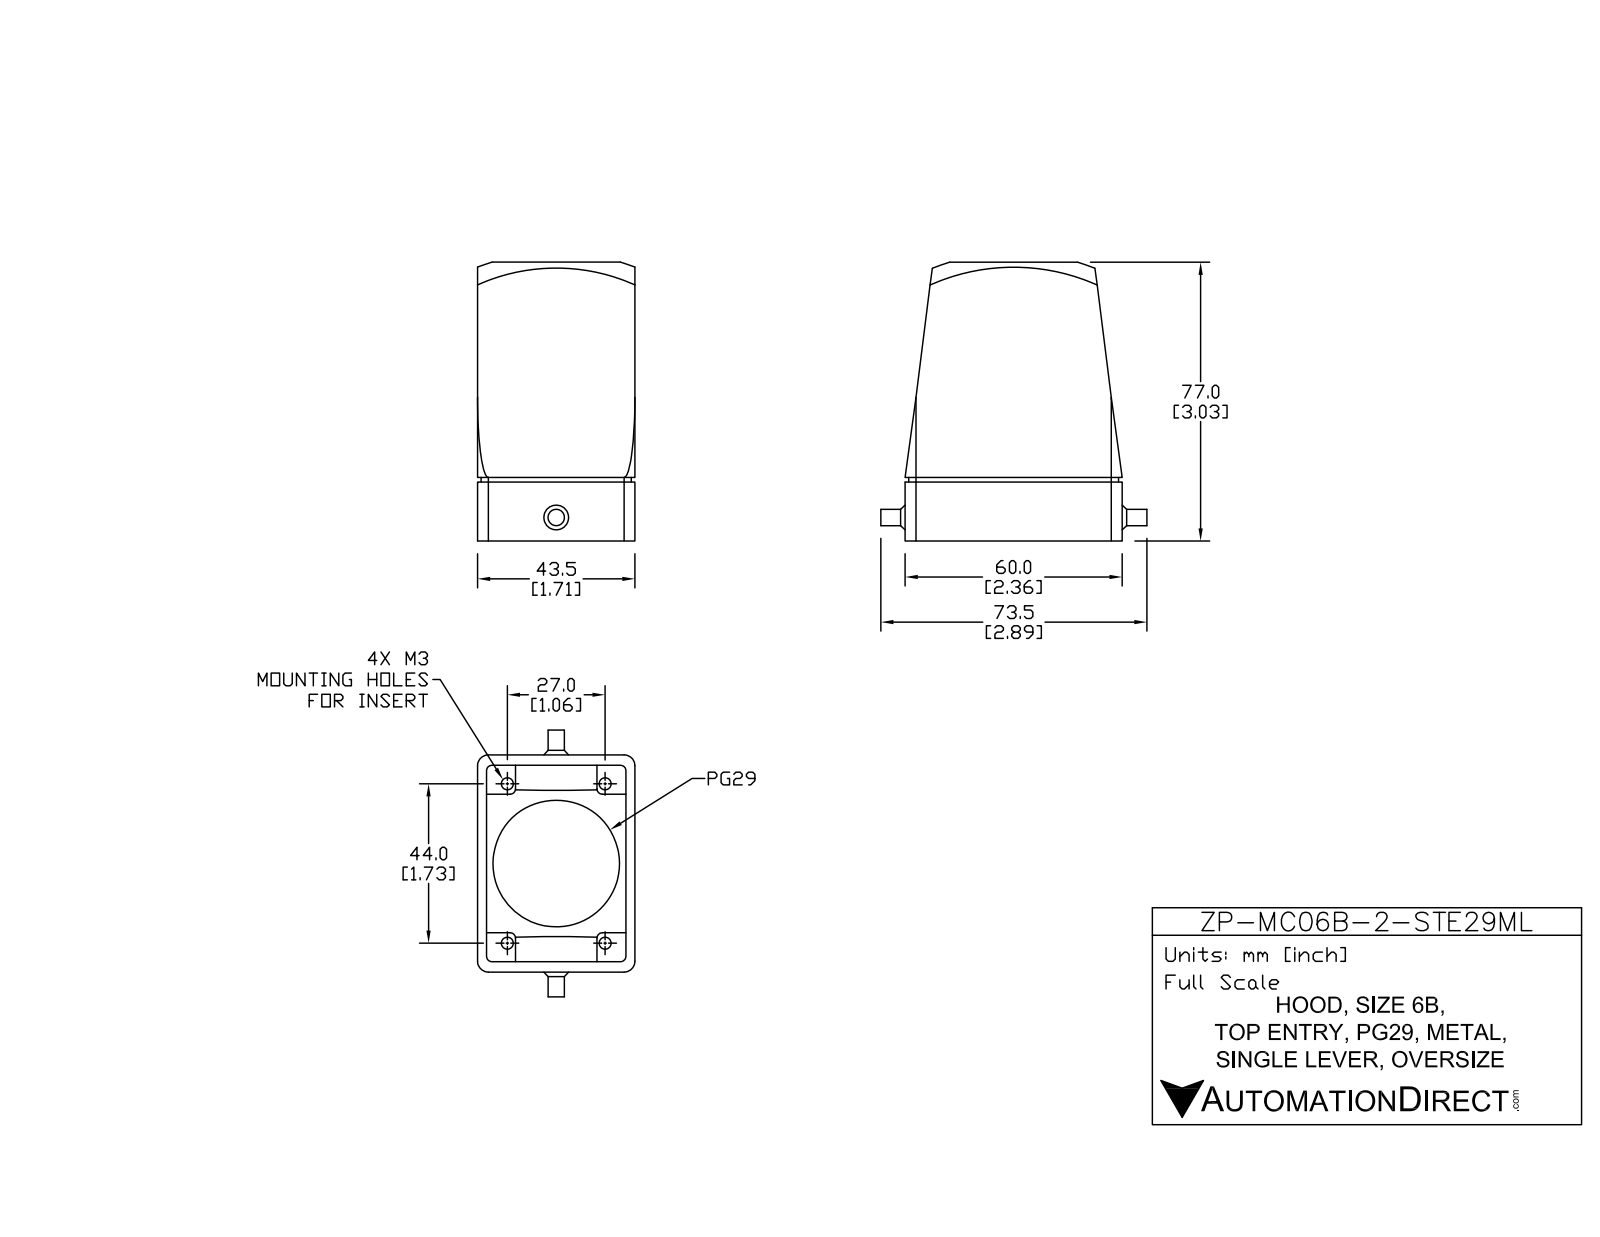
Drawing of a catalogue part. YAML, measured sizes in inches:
part_name: "ZP-MC06B-2-STE29ML"
step_written_by: "SolidWorks 2017 (AUTOMOTIVE_DESIGN)"
units: inches
bodies: {solids: 3, faces: 81, planar: 41, cylindrical: 34, other: 6}
overall_size: [2.952, 2.902, 1.713]
volume: 2.769
surface_area: 46.69
round_holes:
  - {diameter: 0.138, count: 4}
  - {diameter: 1.378, count: 1}
round_bosses_or_shafts:
  - {diameter: 0.178, count: 1}
partial_cylinders:
  - {radius: 0.059, count: 8}
  - {radius: 0.079, count: 4}
  - {radius: 0.118, count: 4}
face_to_face_distances: [0.098, 1.614, 1.713, 1.516, 0.315, 0.428, 1.935, 0.113, 2.25, 1.822]
hole_center_spacings: [1.016, 1.063, 1.732, 2.032]
